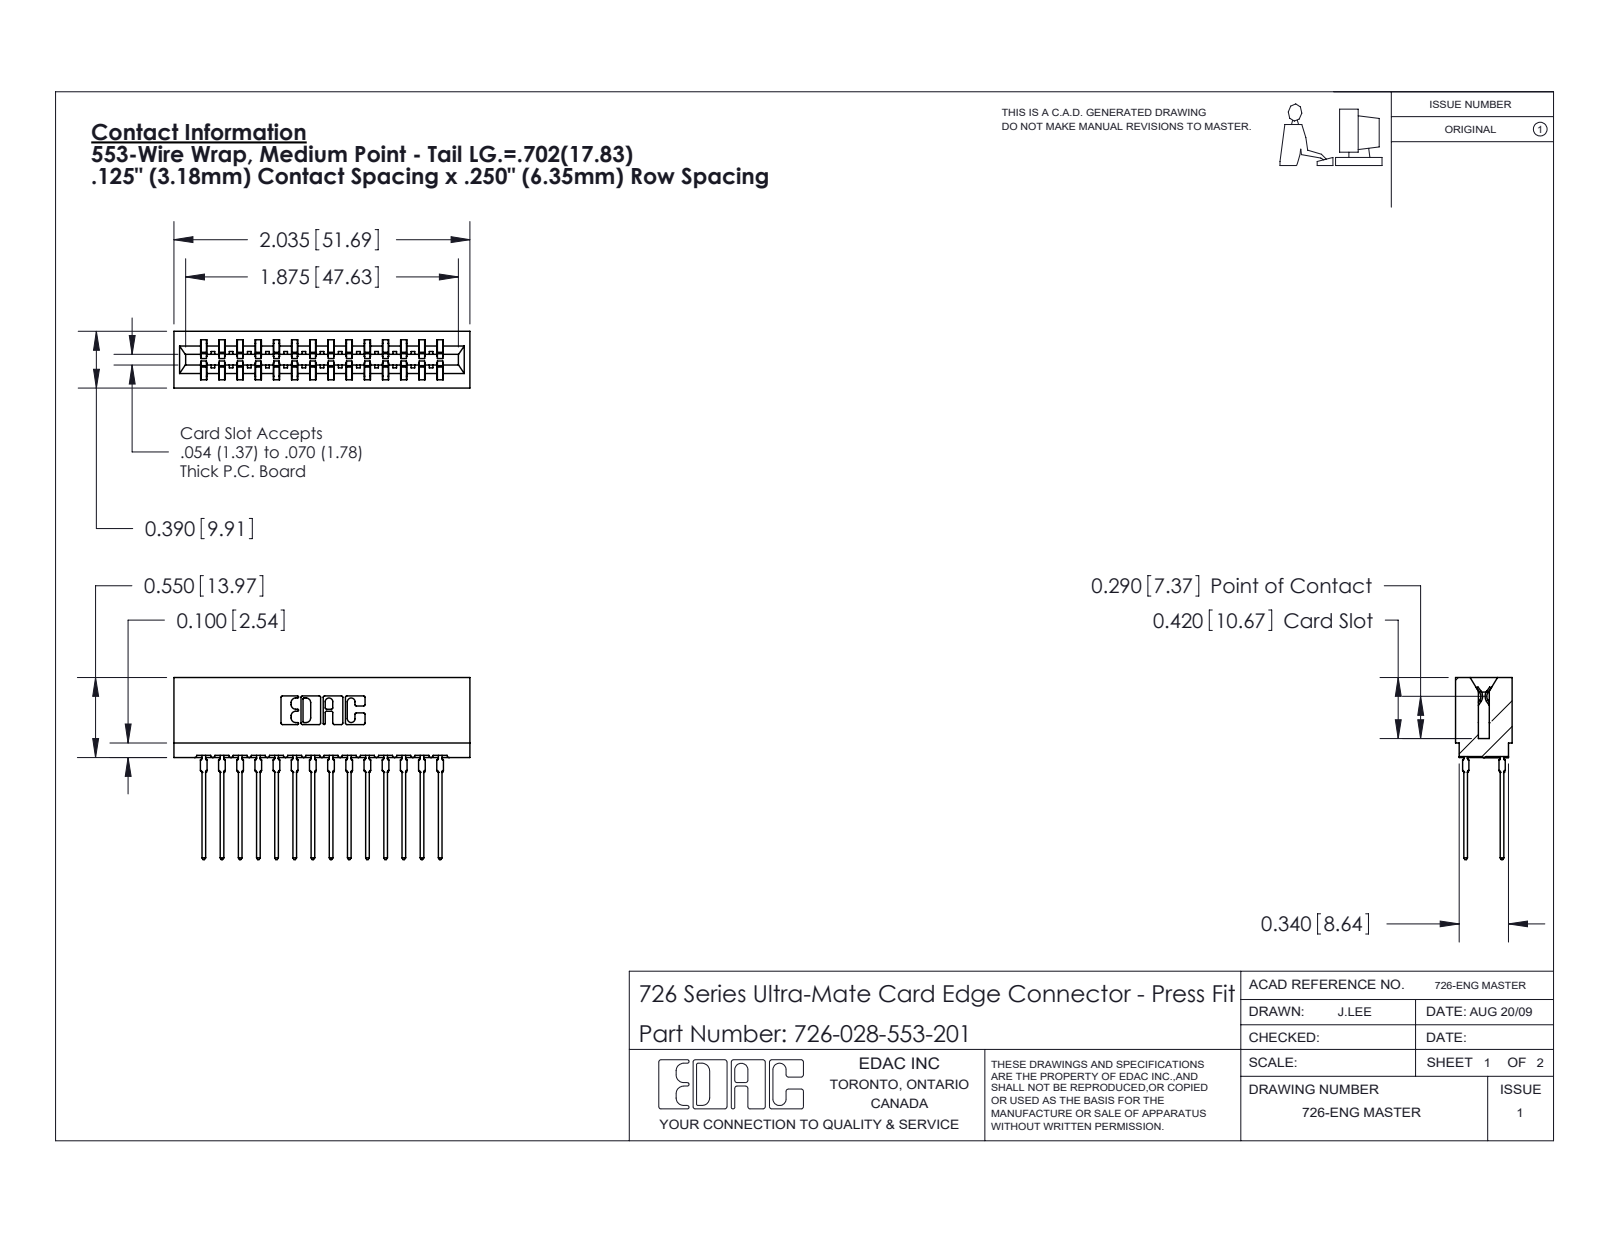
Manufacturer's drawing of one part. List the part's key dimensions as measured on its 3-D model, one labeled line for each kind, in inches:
Part name (STEP PRODUCT): 726-028-553-201; 746-292-001_553; 726 Part_.515 Slot Depth - 01
STEP written by: SolidWorks 2020 (CONFIG_CONTROL_DESIGN)
Units: inches
Bodies: 29 solids, 2603 faces (1343 planar, 532 cylindrical, 728 other)
Overall size (bounding box): 2.035 × 1.251 × 0.39
Volume: 0.307 in³ · Surface area: 13.1 in²
Partial cylindrical surfaces — rounded edges, fillets, slot ends (radius × count): R0.021 ×56, R0.01 ×22, R0.015 ×15, R0.005 ×8, R0.011 ×8, R0.007 ×6, R0.031 ×6, R0.026 ×3
Main face-to-face distances: 0.057, 0.25, 0.333, 0.025, 0.307, 0.083, 0.39, 0.275, 0.125, 0.75
